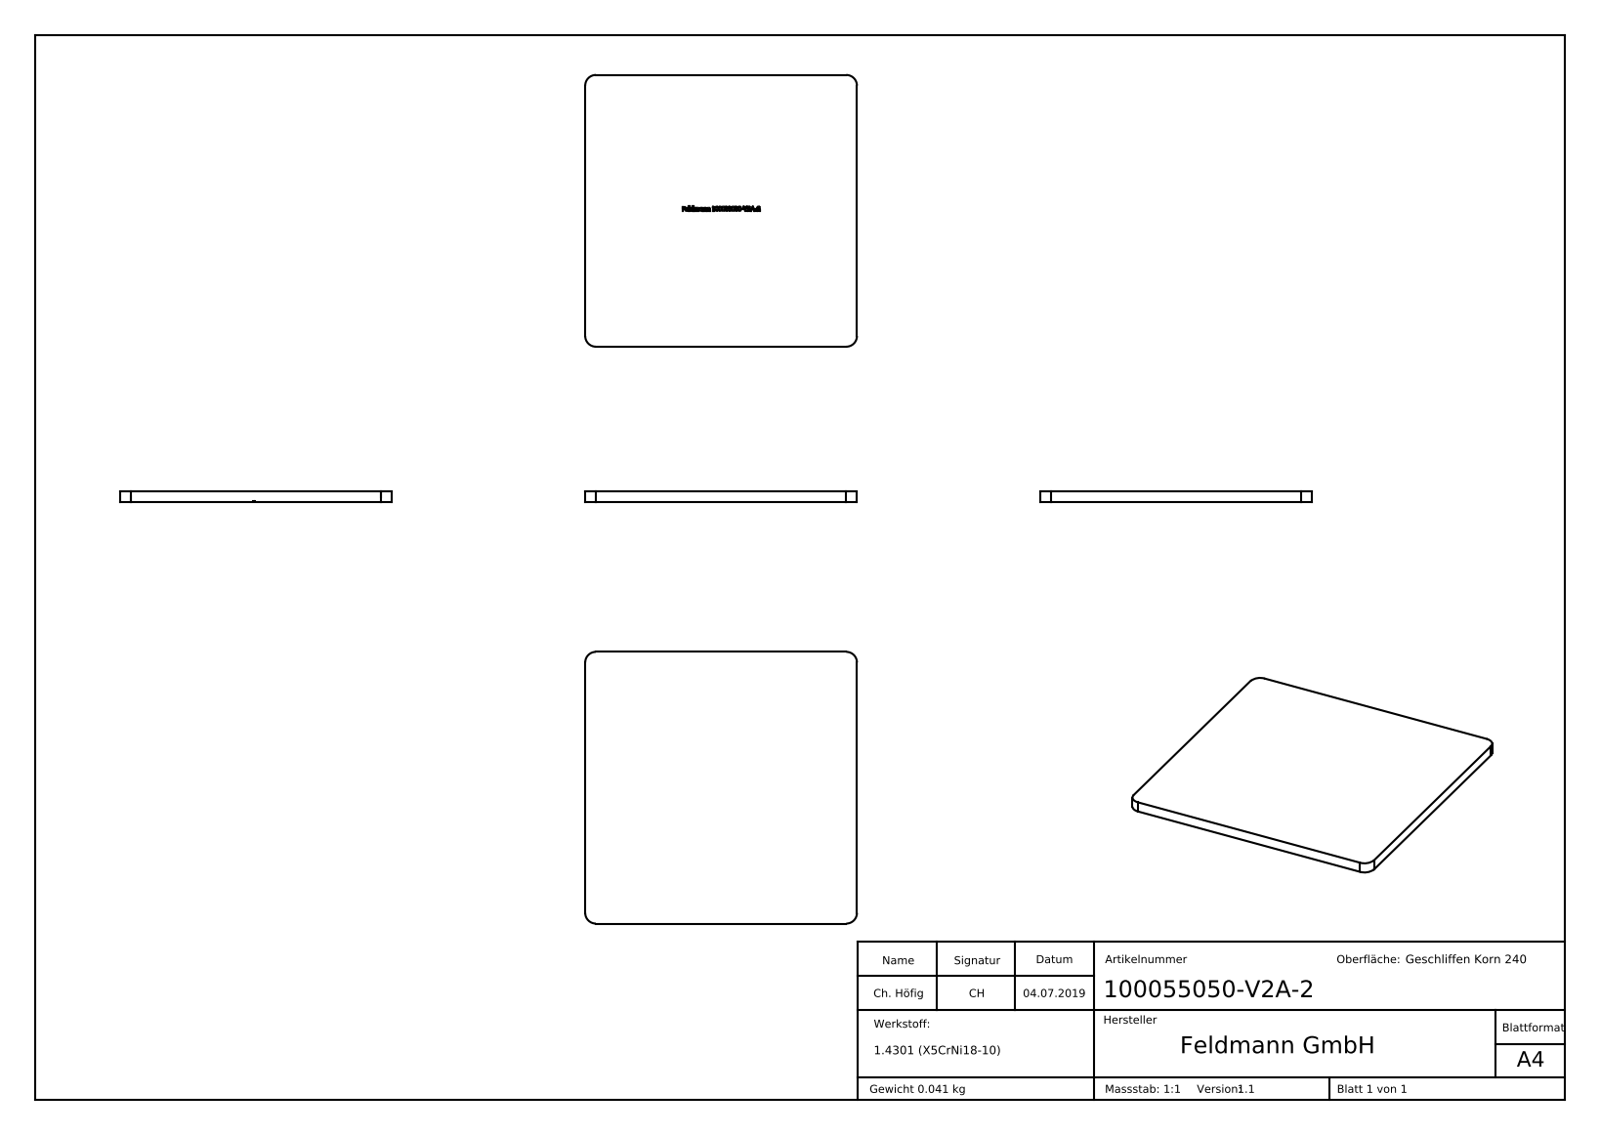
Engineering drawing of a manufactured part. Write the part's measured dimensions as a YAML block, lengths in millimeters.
part_name: "100055050-V2A-2"
step_written_by: "SolidWorks 2015 (CONFIG_CONTROL_DESIGN)"
units: millimeters
bodies: {solids: 1, faces: 287, planar: 154, cylindrical: 4, other: 129}
overall_size: [51, 51, 2]
volume: 5195
surface_area: 5604
partial_cylinders:
  - {radius: 2, count: 4}
face_to_face_distances: [2, 51, 1.9, 25.5, 1.78, 0.71, 1.85, 0.75, 26.29, 0.79]
